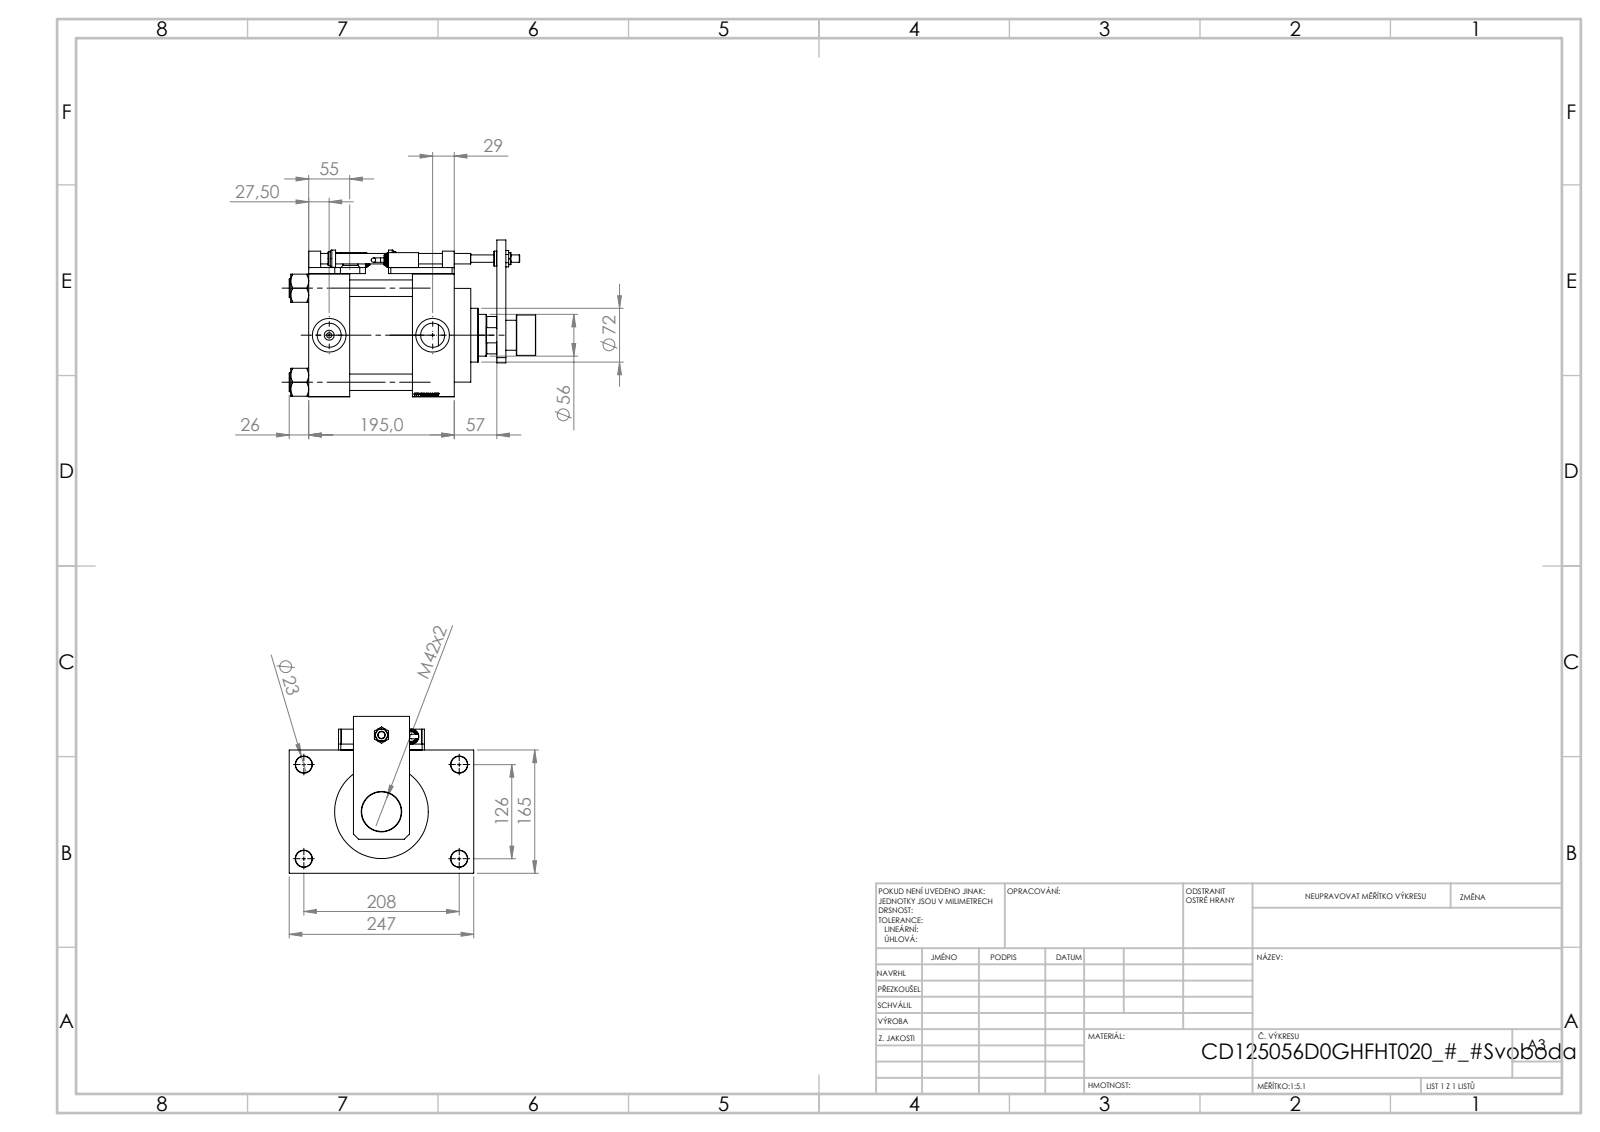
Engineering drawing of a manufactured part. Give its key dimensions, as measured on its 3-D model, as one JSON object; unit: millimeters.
{"part_name": "V215CD_NUT_M5_D; V215CD_SWITCH_Q_SWITCH; V215CD_SWITCH_Q_NUT; V215CR_ROD_END_F (+7 more)", "step_written_by": "SolidWorks 2019 (CONFIG_CONTROL_DESIGN)", "units": "millimeters", "bodies": {"solids": 25, "faces": 1390, "planar": 669, "cylindrical": 158, "other": 563}, "overall_size": [330, 247, 210], "volume_mm3": 5389000, "surface_area_mm2": 652831, "round_holes": [[22, 8], [8.5, 4], [13.5, 4], [7, 2], [32.24, 2], [45, 2], [10, 1], [14, 1], [40.5, 1], [42, 1], [56, 1], [59, 1]], "round_bosses_or_shafts": [[25, 4], [20, 3], [16, 2], [14, 2], [6, 2], [131, 1], [72, 1], [54, 1]], "partial_cylinders_radius": [[7.5, 4]], "face_to_face_distances": [165, 140, 55, 139, 195, 84, 56, 173, 8, 41], "hole_center_spacings": [41.05, 89.02, 121.59, 125.9, 132.47, 166.95, 209.13, 32]}
